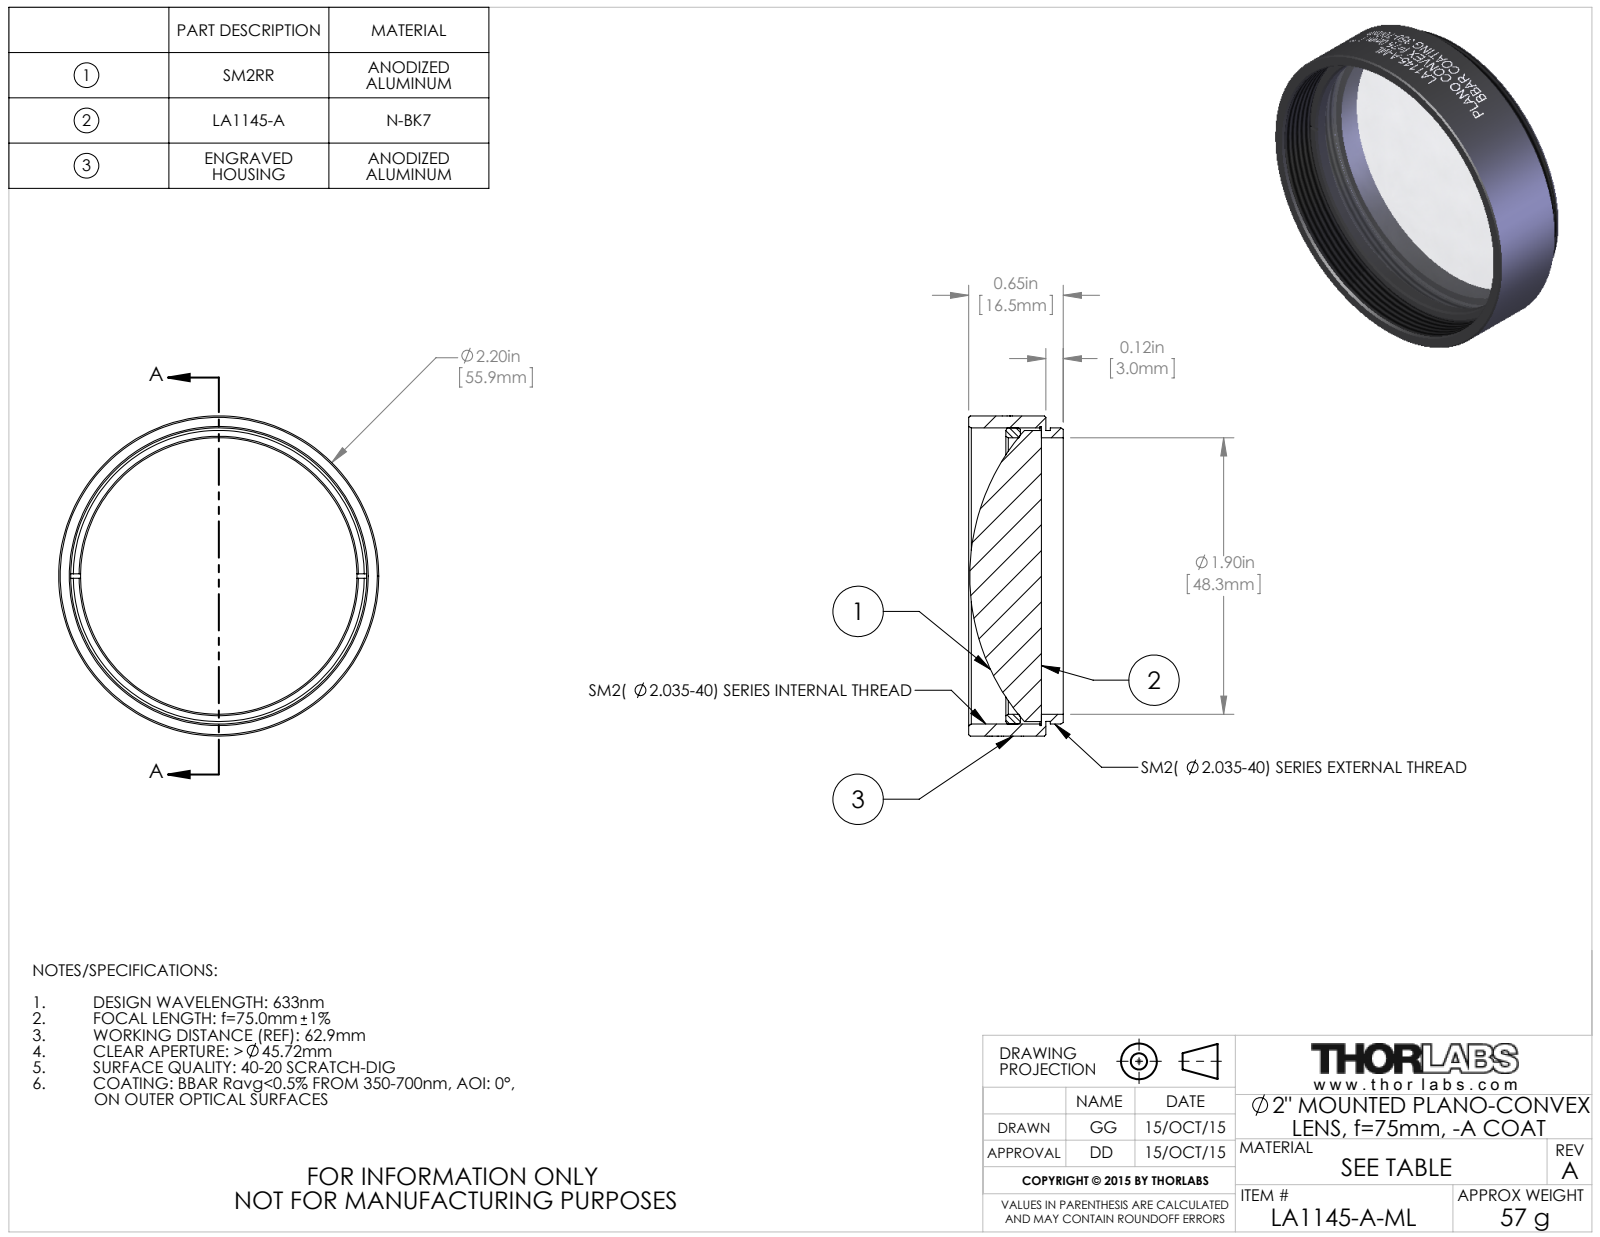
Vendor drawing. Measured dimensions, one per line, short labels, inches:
name: TTN039511-E0W
written by: SolidWorks 2014 (CONFIG_CONTROL_DESIGN)
unit: in
bodies: 3 solids, 141 faces (16 planar, 105 cylindrical, 20 other)
size: 2.2 × 2.2 × 0.65
volume: 1.374 in³; area: 19.99 in²
holes: 1× ⌀1.9, 1× ⌀2.055
bosses: 1× ⌀2.2, 1× ⌀2.035, 1× ⌀2, 1× ⌀1.999
face distances: 0.03, 0.5, 0.53, 0.65, 0.15, 0.12, 0.355, 0.145, 0.176, 0.295
